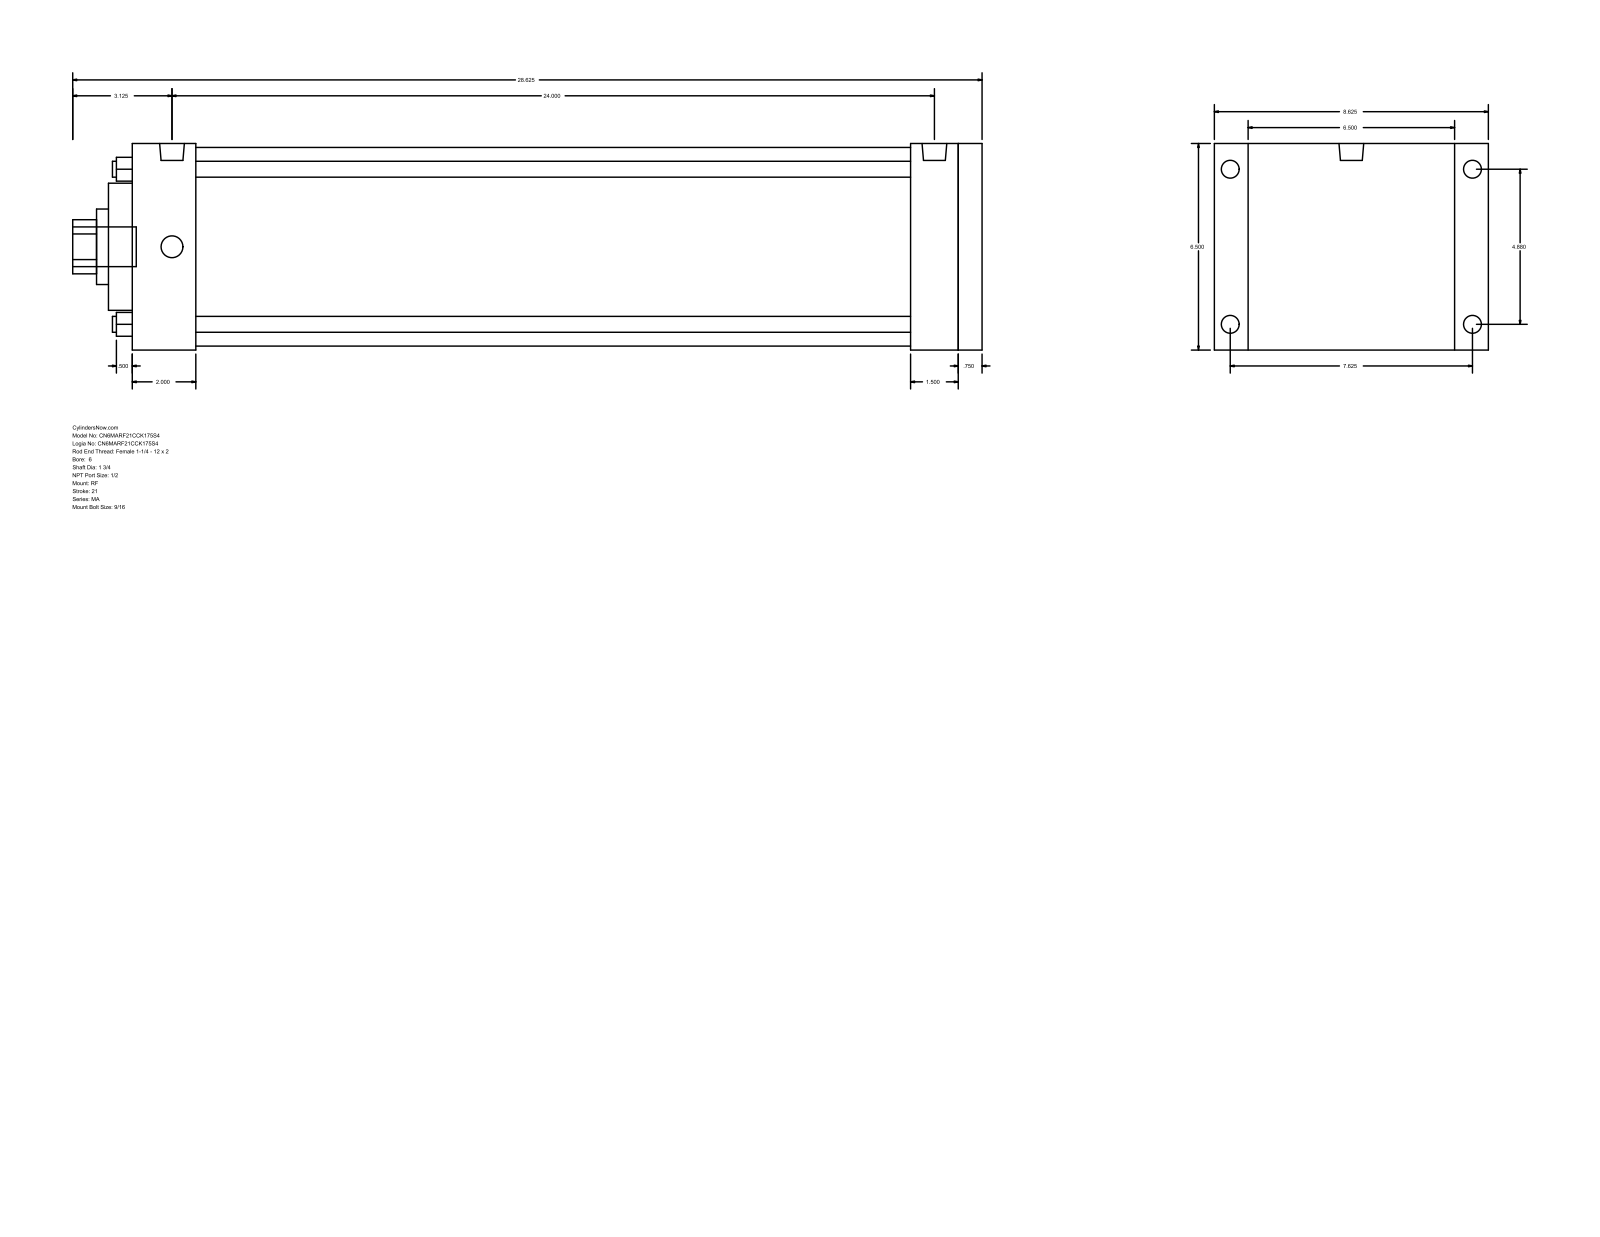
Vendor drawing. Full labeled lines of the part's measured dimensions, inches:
Part name (STEP PRODUCT): MA_RF__0600_1.75
STEP written by: GSSL Pune (CONFIG_CONTROL_DESIGN)
Units: inches
Bodies: 0 solids, 94 faces (65 planar, 29 cylindrical, 0 other)
Overall size (bounding box): 28.625 × 8.625 × 6.5
Round holes (diameter × count): ⌀0.5 ×4, ⌀1.75 ×1, ⌀2.375 ×1, ⌀4 ×1, ⌀6.25 ×1
Round bosses / shafts (diameter × count): ⌀0.687 ×4, ⌀0.563 ×4, ⌀0.778 ×2, ⌀1.25 ×1
Partial cylindrical surfaces — rounded edges, fillets, slot ends (radius × count): R0.852 ×1
Main face-to-face distances: 6.5, 26.75, 26, 0.75, 0.75, 1.5, 2, 24, 24.75, 24.5
Hole centre spacings: 3.451, 4.88, 6.902
